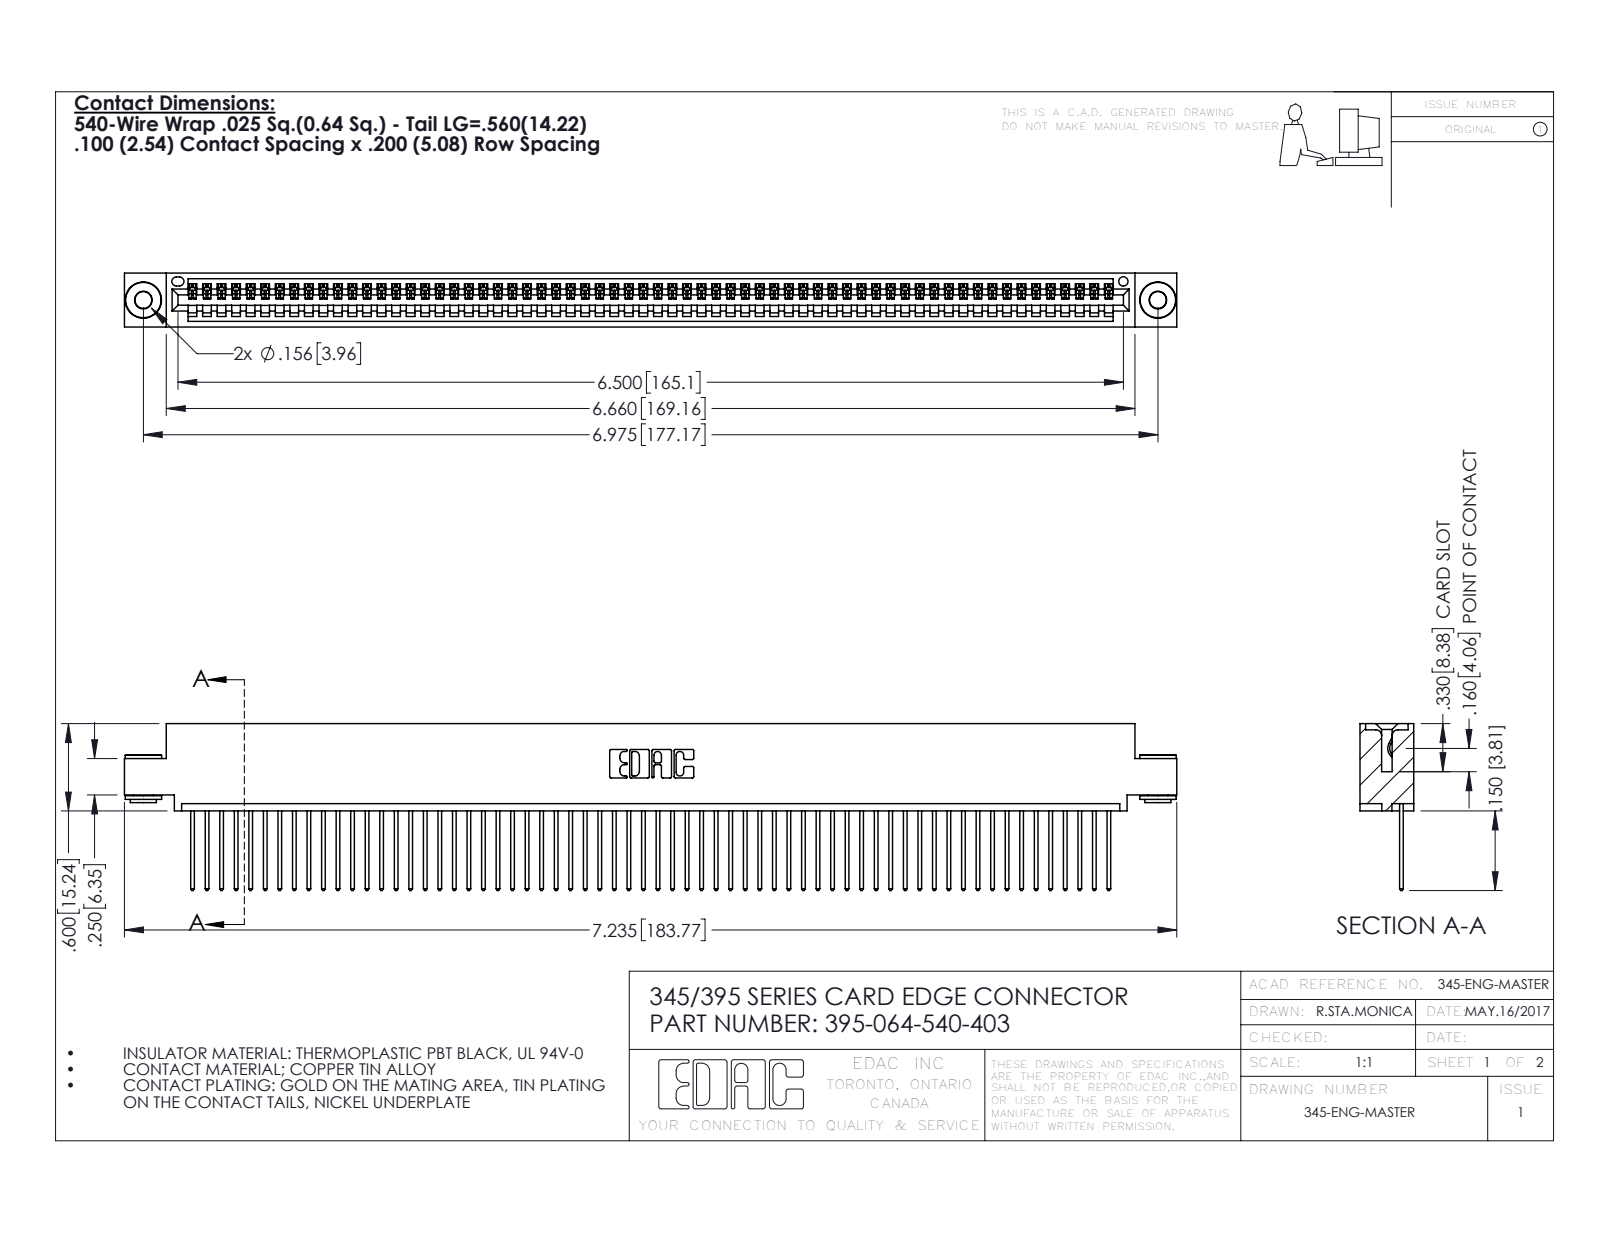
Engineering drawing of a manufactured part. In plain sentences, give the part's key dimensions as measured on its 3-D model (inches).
The part is named "345-292-001_345-293-140; 345 Part_0.110 Offset - 0.156 Dia-TH; 395-064-540-403; 345-250-002_345-250-002-102". Its 3-D file was written by "SolidWorks 2016 (CONFIG_CONTROL_DESIGN)". It is 67 solids with 3880 faces: 2654 planar, 1218 cylindrical and 8 other. Overall it measures 7.235 by 1.147 by 0.37 inches. Its volume is 1.078 cubic inches and its surface area 38.28 square inches. Round holes: 2 of diameter 0.116, 2 of diameter 0.156, 1 of diameter 0.064. Round bosses or shafts: 2 of diameter 0.25, 2 of diameter 0.18, 2 of diameter 0.136. Partial cylindrical surfaces (rounded edges, fillets, slot ends): 128 of radius 0.006, 128 of radius 0.01, 22 of radius 0.01, 6 of radius 0.007, 6 of radius 0.031, 3 of radius 0.026, 2 of radius 0.031, 2 of radius 0.04. The main face-to-face distances are 0.072, 0.298, 0.025, 0.37, 0.098, 0.272, 0.2, 0.225, 0.149, 0.072. The hole center spacings are 0.27, 6.739, 6.975.
